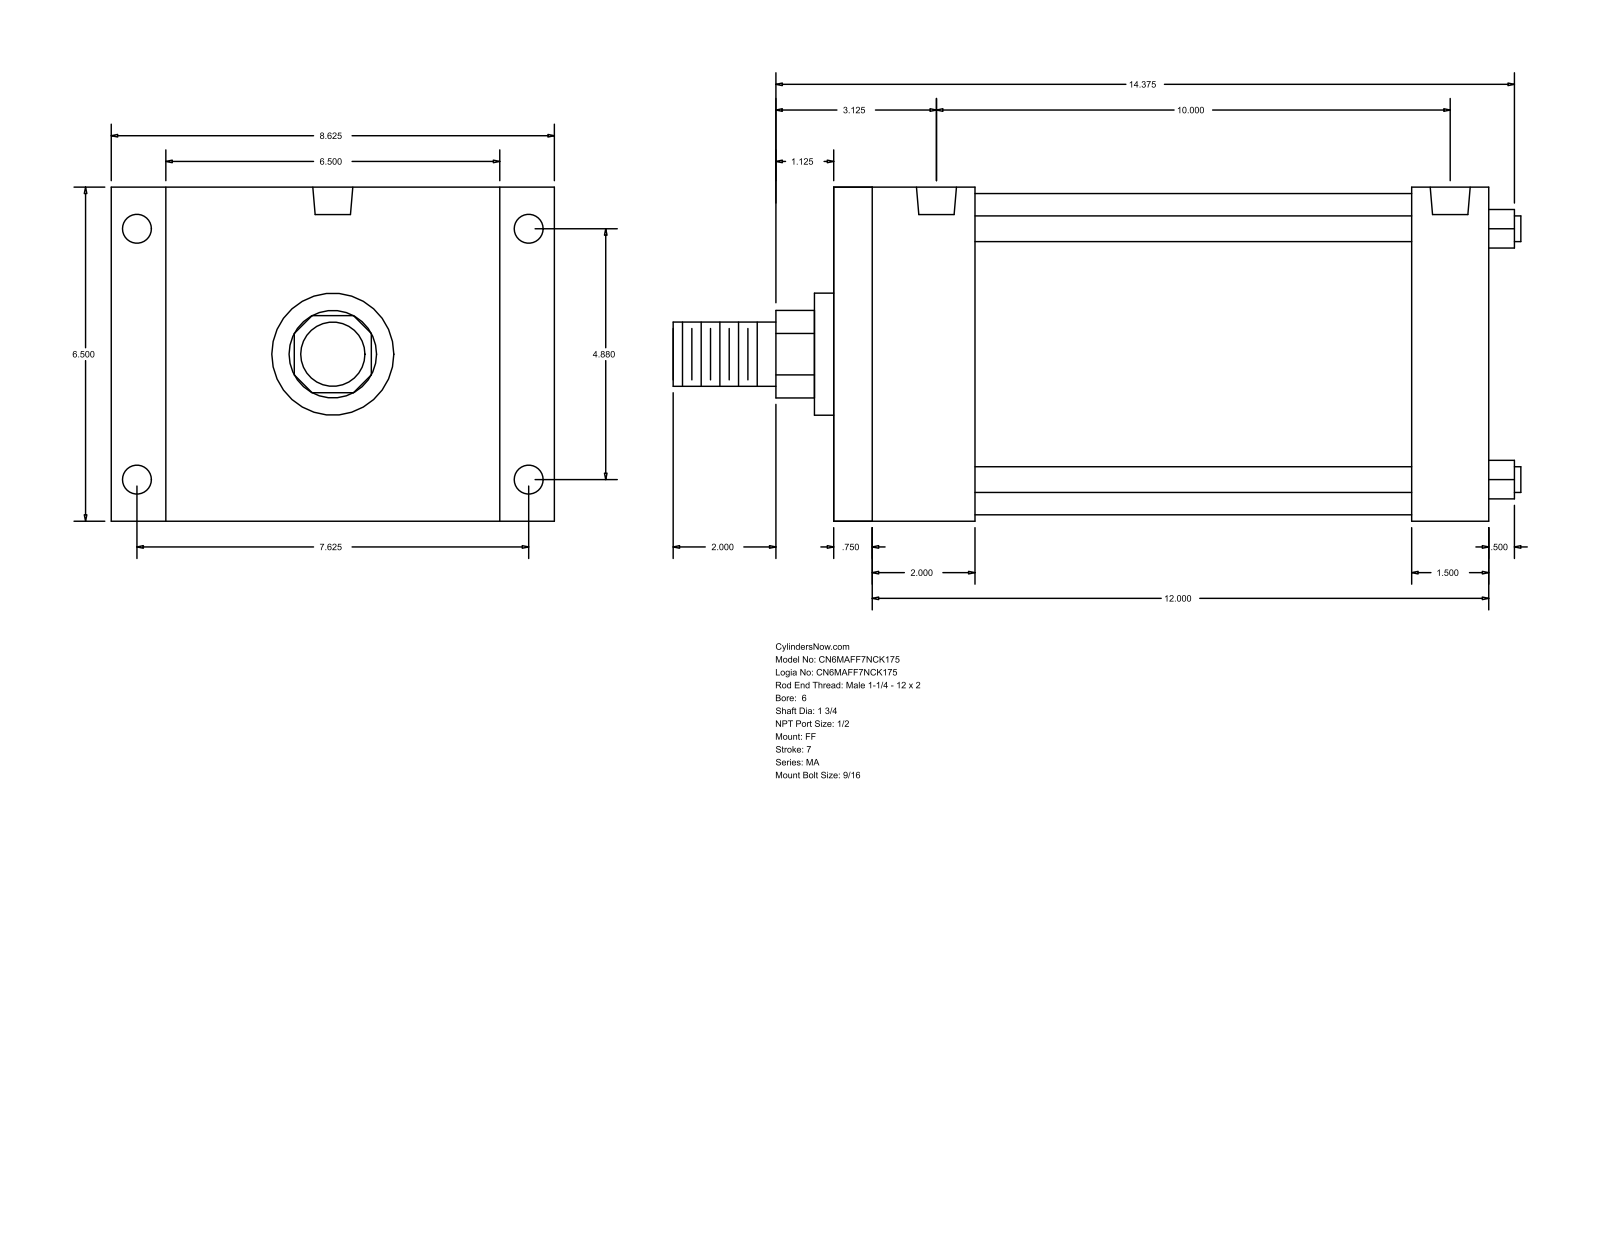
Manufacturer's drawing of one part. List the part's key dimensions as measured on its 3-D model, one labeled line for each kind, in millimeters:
Part name (STEP PRODUCT): MA_FF__0600_1.75
STEP written by: GSSL Pune (CONFIG_CONTROL_DESIGN)
Units: millimetres
Bodies: 0 solids, 92 faces (64 planar, 28 cylindrical, 0 other)
Overall size (bounding box): 419.1 × 219.07 × 165.1
Round holes (diameter × count): ⌀14.29 ×4, ⌀17.46 ×4, ⌀19.77 ×2
Round bosses / shafts (diameter × count): ⌀12.7 ×4, ⌀158.75 ×1, ⌀60.33 ×1, ⌀44.45 ×1, ⌀31.75 ×1
Partial cylindrical surfaces — rounded edges, fillets, slot ends (radius × count): R21.63 ×1
Main face-to-face distances: 165.1, 323.86, 19.05, 304.81, 50.8, 69.85, 266.7, 254.01, 285.75, 215.9
Hole centre spacings: 123.96, 193.68, 229.95, 254
